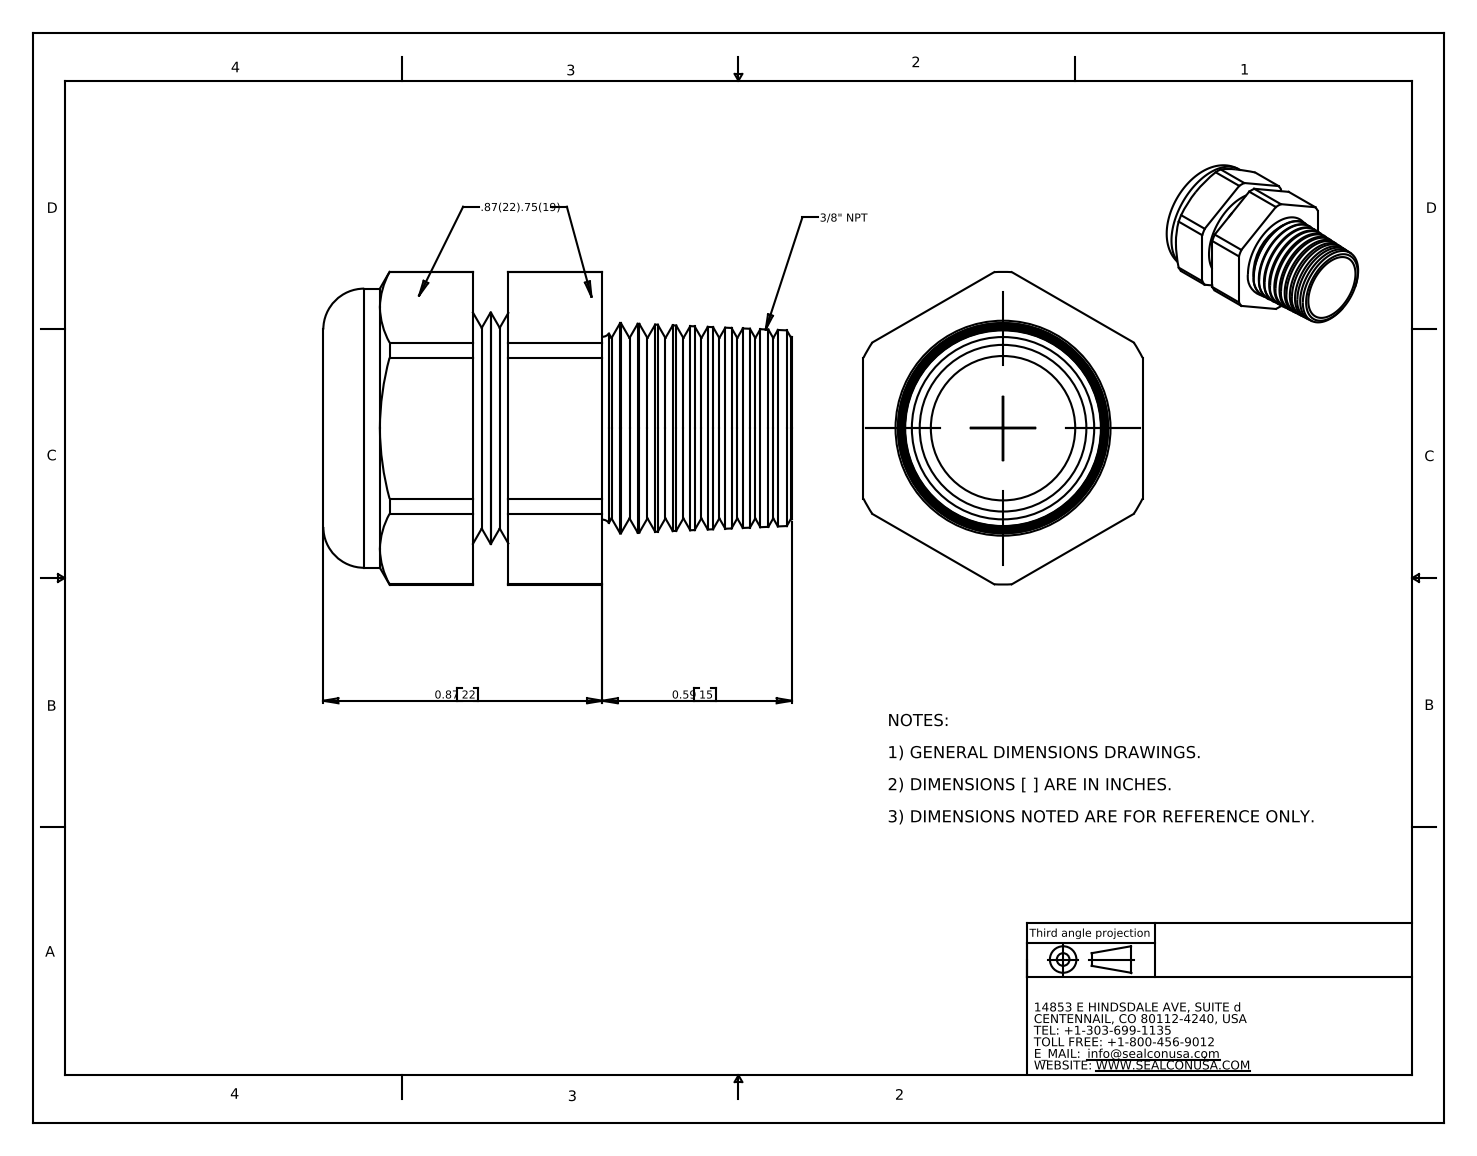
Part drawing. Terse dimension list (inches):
name: CD09NA-BK
written by: SolidWorks 2007 (CONFIG_CONTROL_DESIGN)
unit: in
bodies: 2 solids, 134 faces (20 planar, 26 cylindrical, 88 other)
size: 1.46 × 0.974 × 0.87
volume: 0.424 in³; area: 8.789 in²
holes: 1× ⌀0.45, 1× ⌀0.561, 1× ⌀0.721
bosses: 1× ⌀0.87
rounds: 1× R0.487
face distances: 0.87, 0.11, 0.404, 0.294, 0.29, 0.4, 0.694, 0.156, 0.446, 0.556
